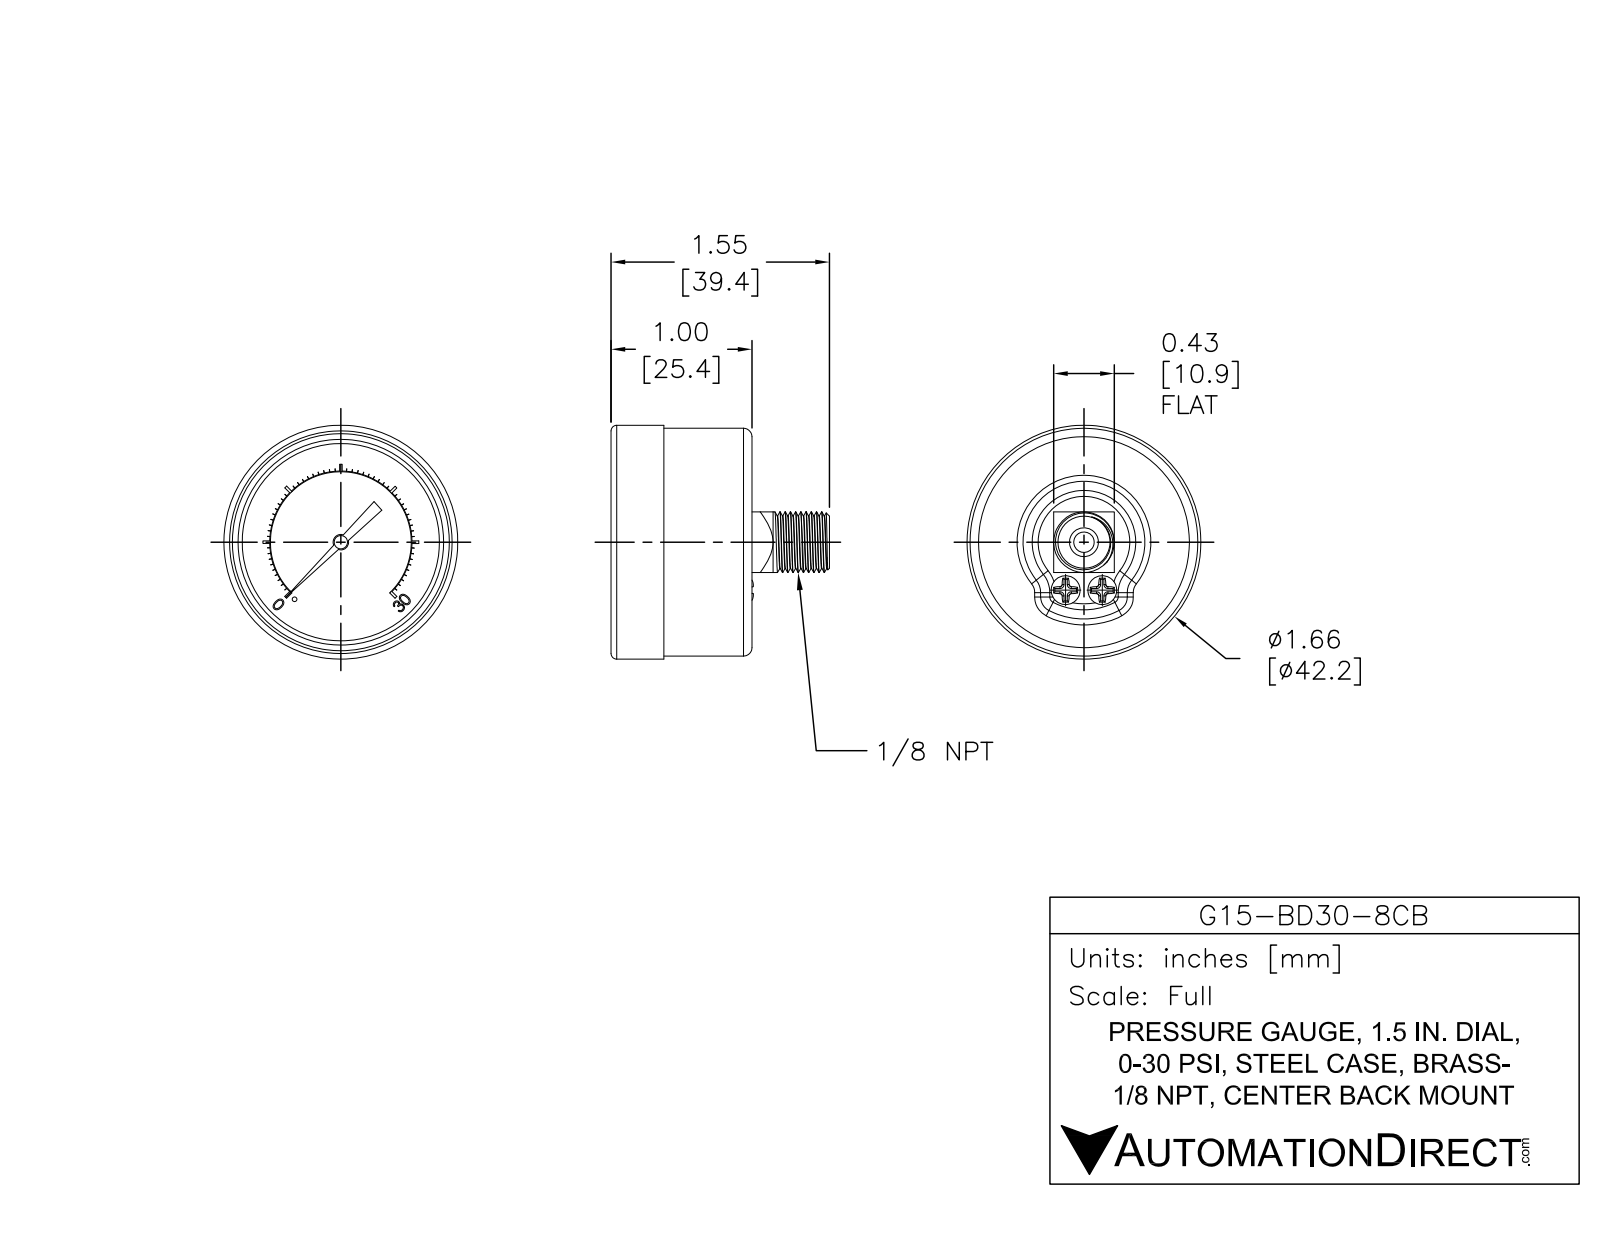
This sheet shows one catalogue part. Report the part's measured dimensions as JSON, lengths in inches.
{"part_name": "G15-BD30-8CB", "step_written_by": "SolidWorks 2021 (AUTOMOTIVE_DESIGN)", "units": "inches", "bodies": {"solids": 1, "faces": 419, "planar": 265, "cylindrical": 85, "other": 69}, "overall_size": [1.66, 1.66, 1.55], "volume_in3": 1.677, "surface_area_in2": 12.03, "round_holes": [[0.145, 1], [1.4, 1]], "round_bosses_or_shafts": [[0.205, 2], [1.66, 1], [1.617, 1], [0.43, 1], [0.086, 1], [0.06, 1], [0.033, 1]], "partial_cylinders_radius": [[0.06, 4], [0.015, 2], [0.048, 1], [0.5, 1], [0.505, 1]], "face_to_face_distances": [0.71, 0.43, 0.1, 0.61, 0.96, 0.86, 0.25, 0.04, 0.625, 0.525]}
